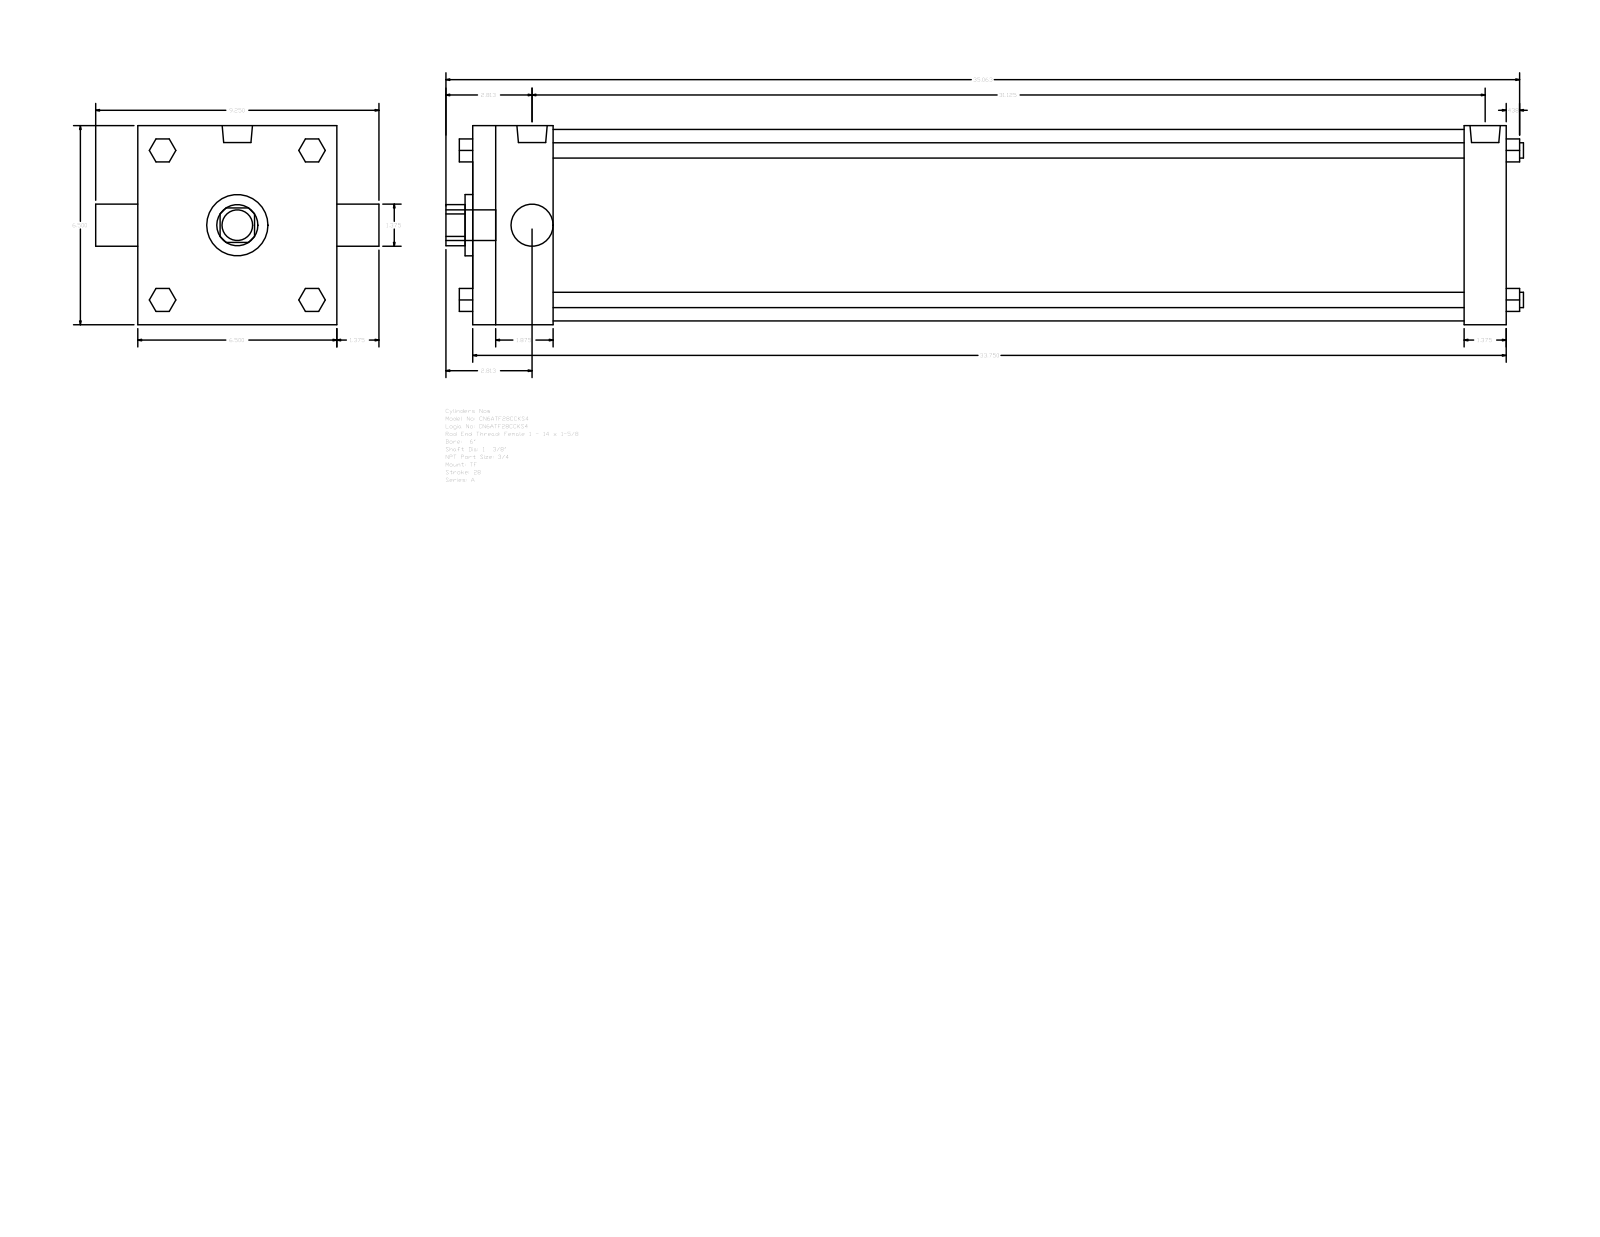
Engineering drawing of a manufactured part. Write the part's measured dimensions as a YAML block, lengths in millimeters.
part_name: "A_TF__0600_1.375"
step_written_by: "GSSL Pune (CONFIG_CONTROL_DESIGN)"
units: millimeters
bodies: {solids: 0, faces: 120, planar: 92, cylindrical: 28, other: 0}
overall_size: [893.76, 234.95, 165.1]
round_holes:
  - {diameter: 34.92, count: 2}
  - {diameter: 50.8, count: 1}
  - {diameter: 158.75, count: 1}
round_bosses_or_shafts:
  - {diameter: 12.7, count: 4}
  - {diameter: 15.08, count: 3}
  - {diameter: 25.12, count: 2}
  - {diameter: 25.4, count: 1}
partial_cylinders:
  - {radius: 17.06, count: 1}
face_to_face_distances: [165.1, 857.25, 66.67, 790.58, 822.32, 755.65, 34.93, 19.05, 61.97, 107.34]
